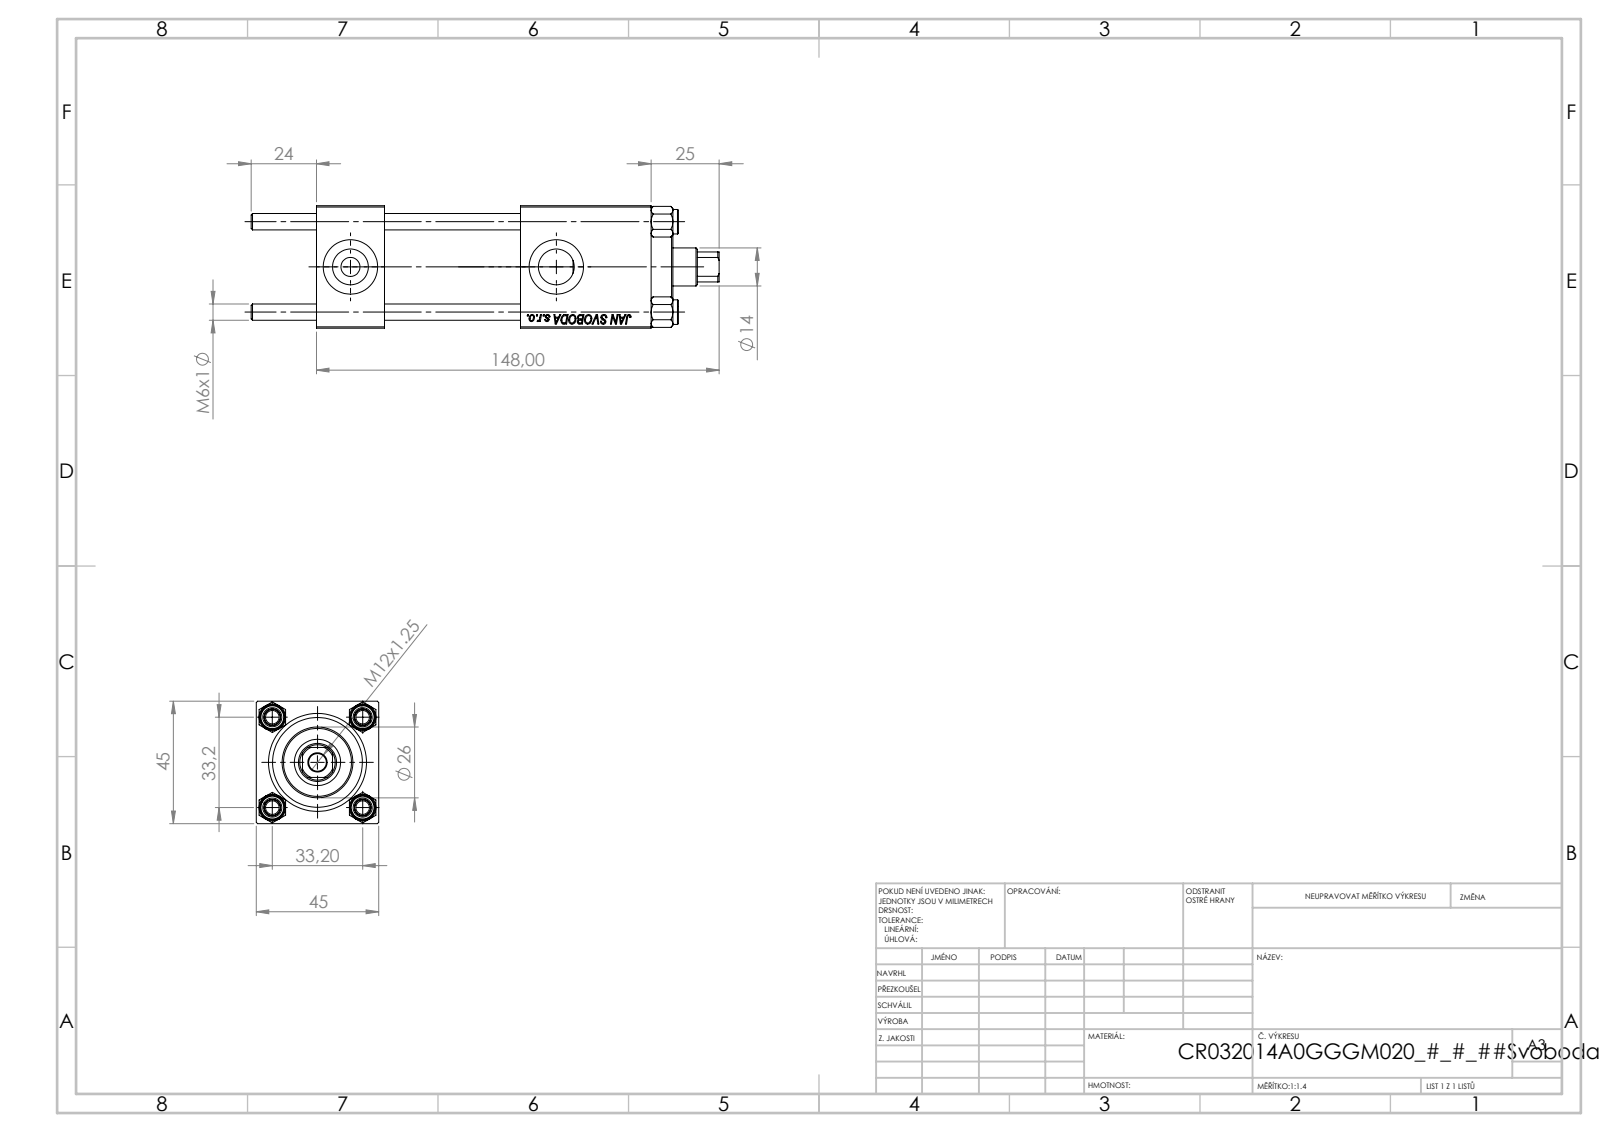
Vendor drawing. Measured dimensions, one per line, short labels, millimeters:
name: V215CR_VCP; V215_VC_A; NUT_M5; V215CR_BODY_A (+1 more)
written by: SolidWorks 2019 (CONFIG_CONTROL_DESIGN)
unit: mm
bodies: 11 solids, 1132 faces (517 planar, 79 cylindrical, 536 other)
size: 172 × 45 × 45
volume: 198 230 mm³; area: 72 807 mm²
holes: 4× ⌀6, 2× ⌀7, 2× ⌀13.16, 2× ⌀20, 1× ⌀6.5, 1× ⌀14, 1× ⌀17, 1× ⌀24, 1× ⌀32, 1× ⌀33
bosses: 4× ⌀9, 1× ⌀38, 1× ⌀26
rounds: 1× R6.5
face distances: 45, 25, 123, 98, 50, 75, 48, 94.3, 69.3, 19.3
hole spacings: 23.48, 33.2, 46.95, 75.66
